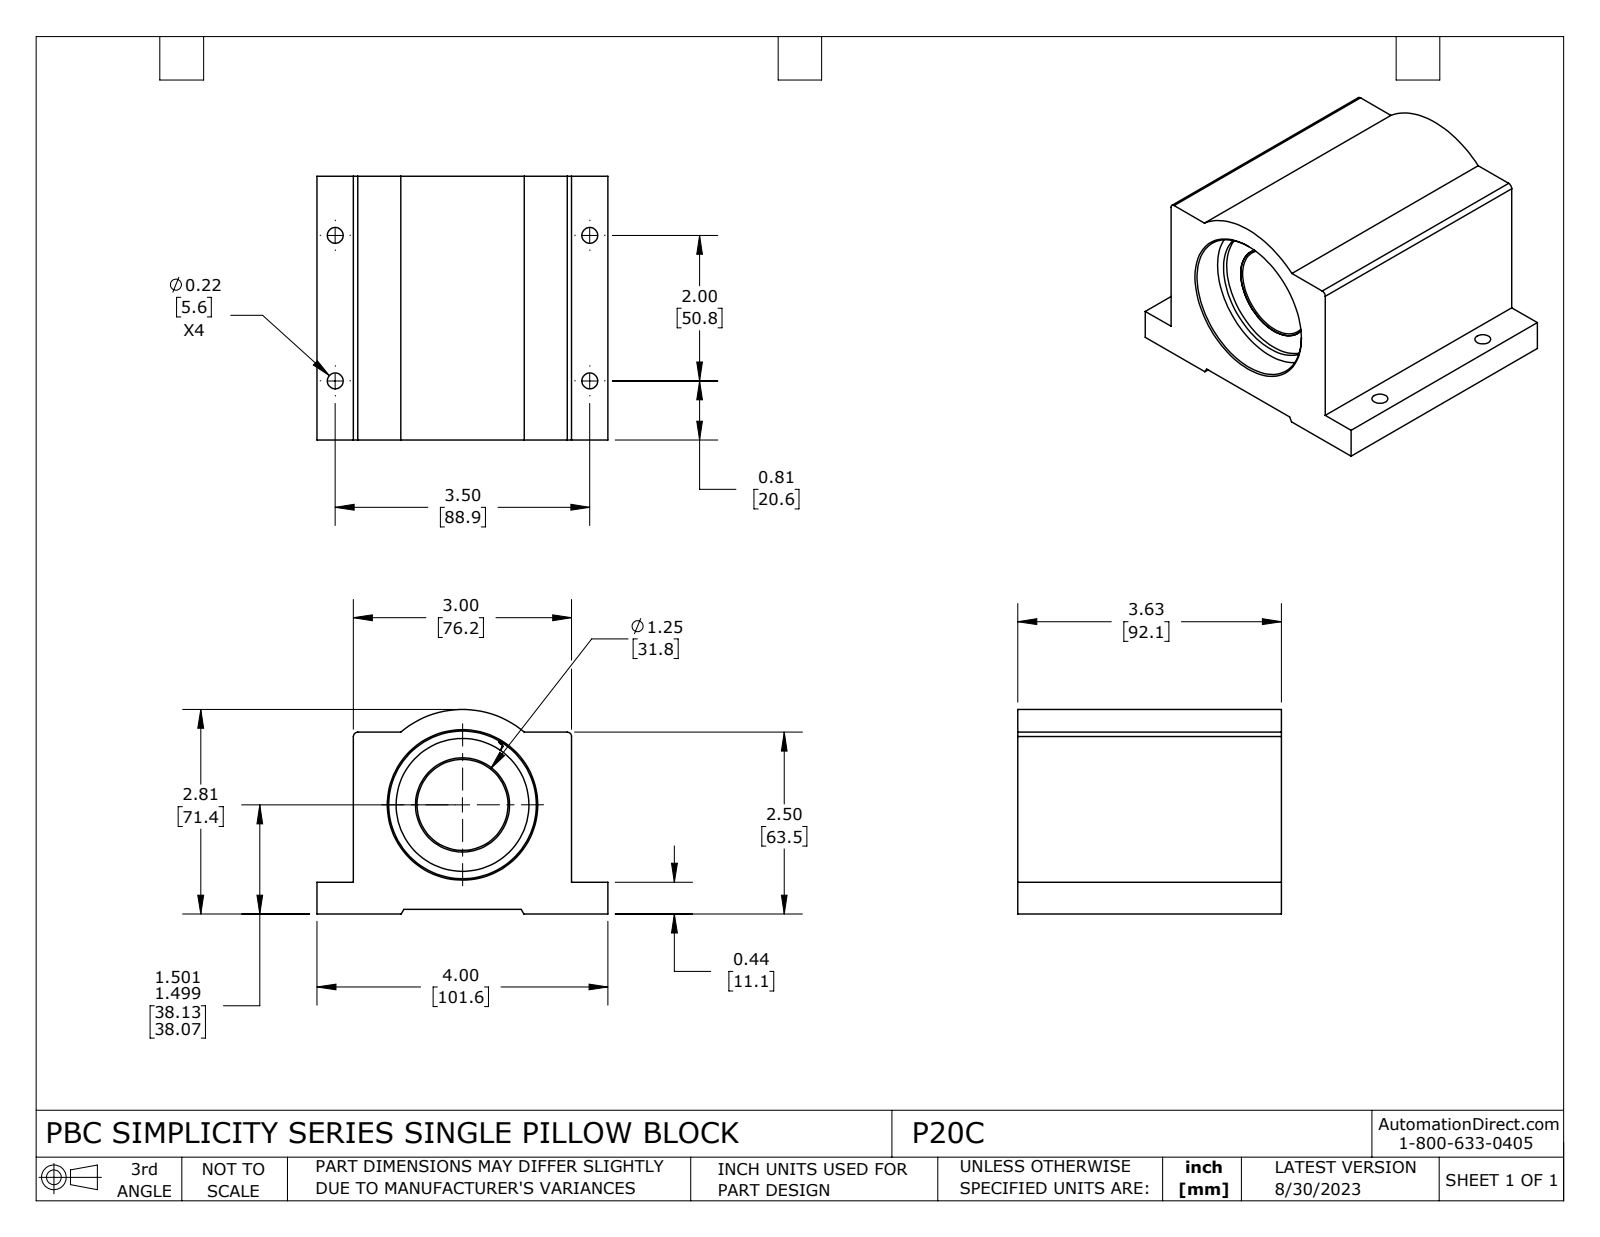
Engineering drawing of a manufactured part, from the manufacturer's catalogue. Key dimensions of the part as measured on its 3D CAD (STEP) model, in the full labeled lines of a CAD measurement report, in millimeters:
Part name (STEP PRODUCT): P20C
STEP written by: SolidWorks 2021 (CONFIG_CONTROL_DESIGN)
Units: millimetres
Bodies: 7 solids, 164 faces (45 planar, 71 cylindrical, 48 other)
Overall size (bounding box): 101.6 × 92.1 × 71.4
Volume: 376 200 mm³ · Surface area: 94 640 mm²
Round holes (diameter × count): ⌀5.6 ×4, ⌀31.8 ×1, ⌀32.9 ×1, ⌀46.4 ×1, ⌀51.5 ×1, ⌀53.9 ×1
Round bosses / shafts (diameter × count): ⌀54.4 ×1, ⌀50.8 ×1, ⌀48 ×1, ⌀46.7 ×1
Partial cylindrical surfaces — rounded edges, fillets, slot ends (radius × count): R0.7 ×4, R0.5 ×2, R0.8 ×2, R1.5 ×2, R33.3 ×1
Main face-to-face distances: 76.2, 1.7, 92.1, 63.5, 61.8, 11.1, 9.4, 52.4, 12.8, 79.3
Hole centre spacings: 50.8, 88.9, 102.4
